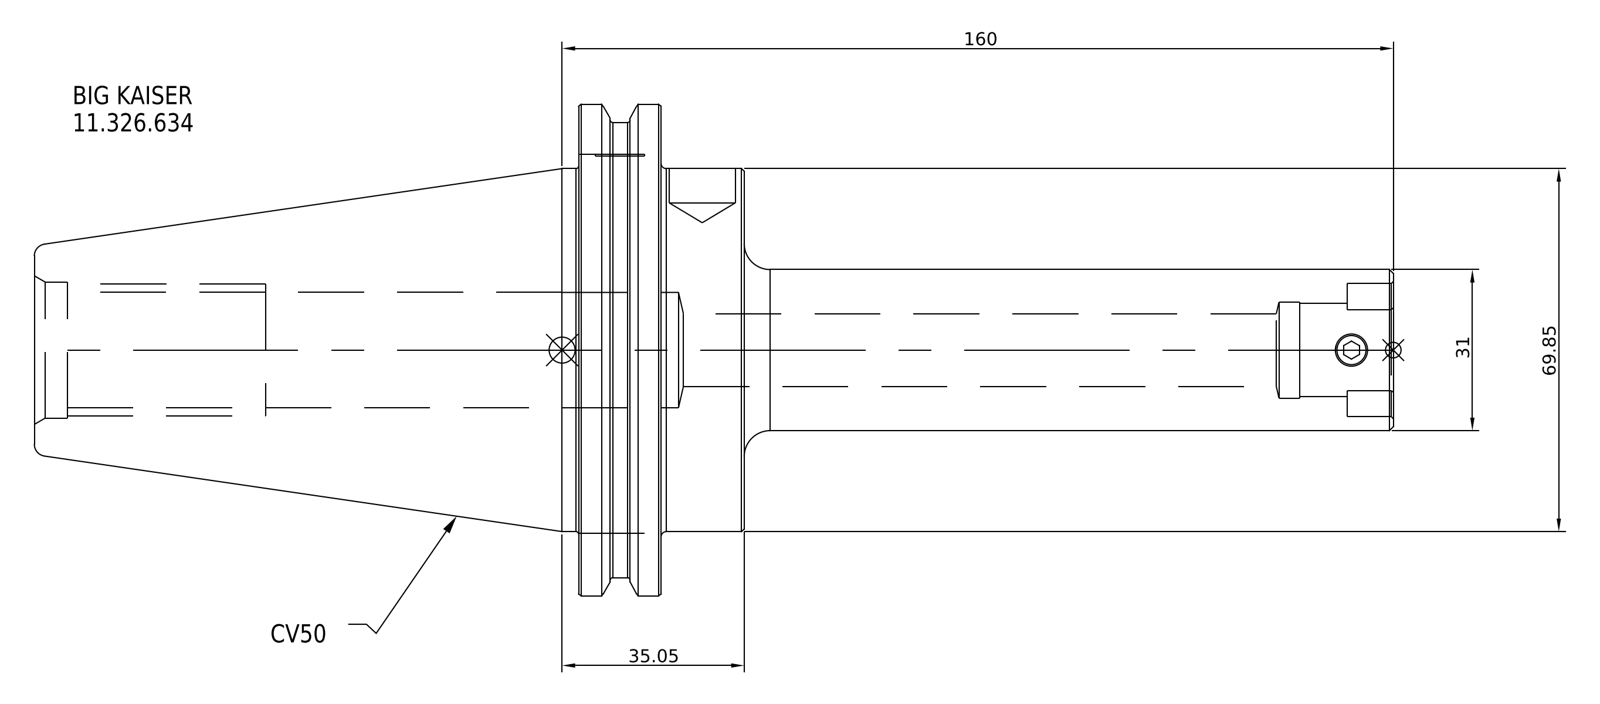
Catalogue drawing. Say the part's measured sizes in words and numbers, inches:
The part is named "11.326.634". Its 3-D file was written by "SolidWorks 2021 (CONFIG_CONTROL_DESIGN)". It is 1 solid with 16 faces: 7 planar, 6 cylindrical and 3 other. Overall it measures 10.299 by 3.875 by 3.875 inches. Its volume is 32.76 cubic inches and its surface area 82.38 square inches. Round bosses or shafts: 1 of diameter 3.875, 1 of diameter 3.594, 1 of diameter 2.75, 1 of diameter 1.22. The main face-to-face distances are 0.691, 0.628, 1.319, 5.378, 4.75, 4.059, 4.921, 5.549, 6.24, 10.299.
